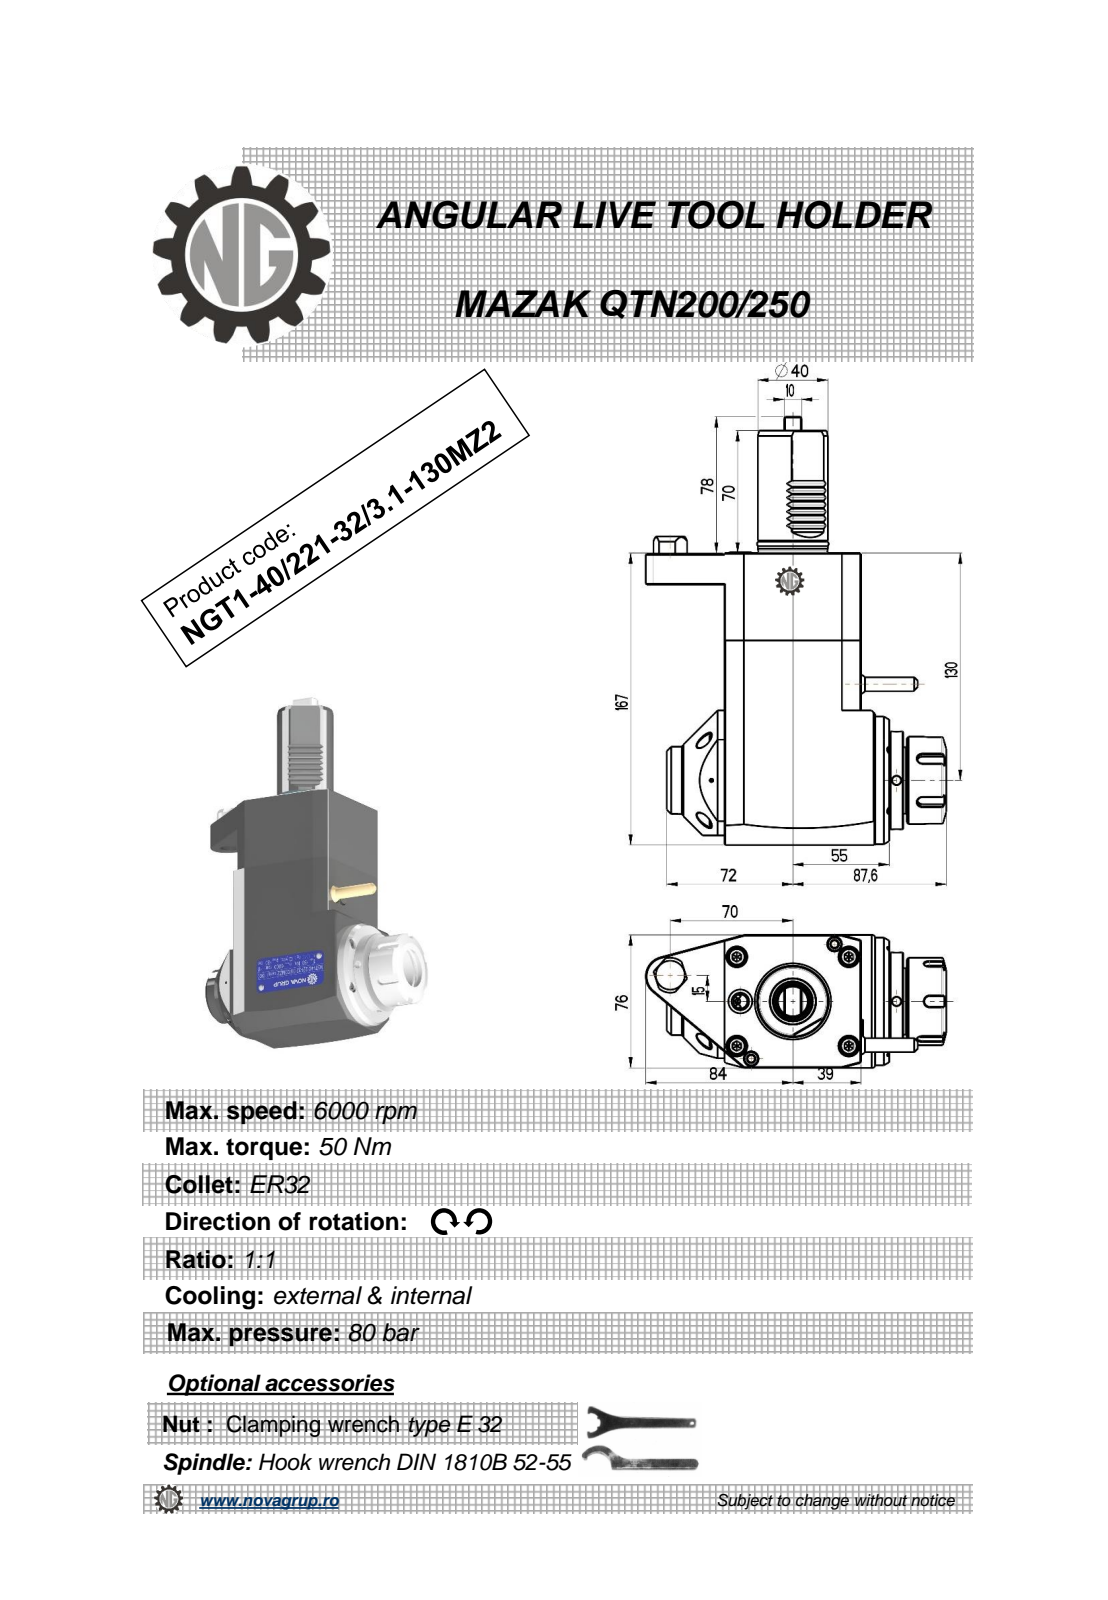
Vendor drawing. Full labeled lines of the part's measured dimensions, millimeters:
Part name (STEP PRODUCT): NGT1_40_221_32_3_1_130MZ2
STEP written by: PRO/ENGINEER BY PARAMETRIC TECHNOLOGY CORPORATION, 2010280 (CONFIG_CONTROL_DESIGN)
Units: millimetres
Bodies: 1 solid, 295 faces (132 planar, 76 cylindrical, 87 other)
Overall size (bounding box): 245 × 171.6 × 76
Volume: 1 312 000 mm³ · Surface area: 93 504 mm²
Round holes (diameter × count): ⌀5 ×3, ⌀3 ×1, ⌀8 ×1, ⌀27 ×1
Round bosses / shafts (diameter × count): ⌀73 ×1, ⌀56 ×1, ⌀50 ×1, ⌀43 ×1, ⌀40 ×1, ⌀39.4 ×1, ⌀38.5 ×1, ⌀36.2 ×1
Partial cylindrical surfaces — rounded edges, fillets, slot ends (radius × count): R0.3 ×7, R0.2 ×6, R3 ×5, R0.8 ×2, R300 ×2, R9 ×1, R10 ×1, R11.35 ×1
Main face-to-face distances: 76, 78, 167, 8, 16, 94, 18, 87.92, 149, 86
Hole centre spacings: 60.42, 89.25
